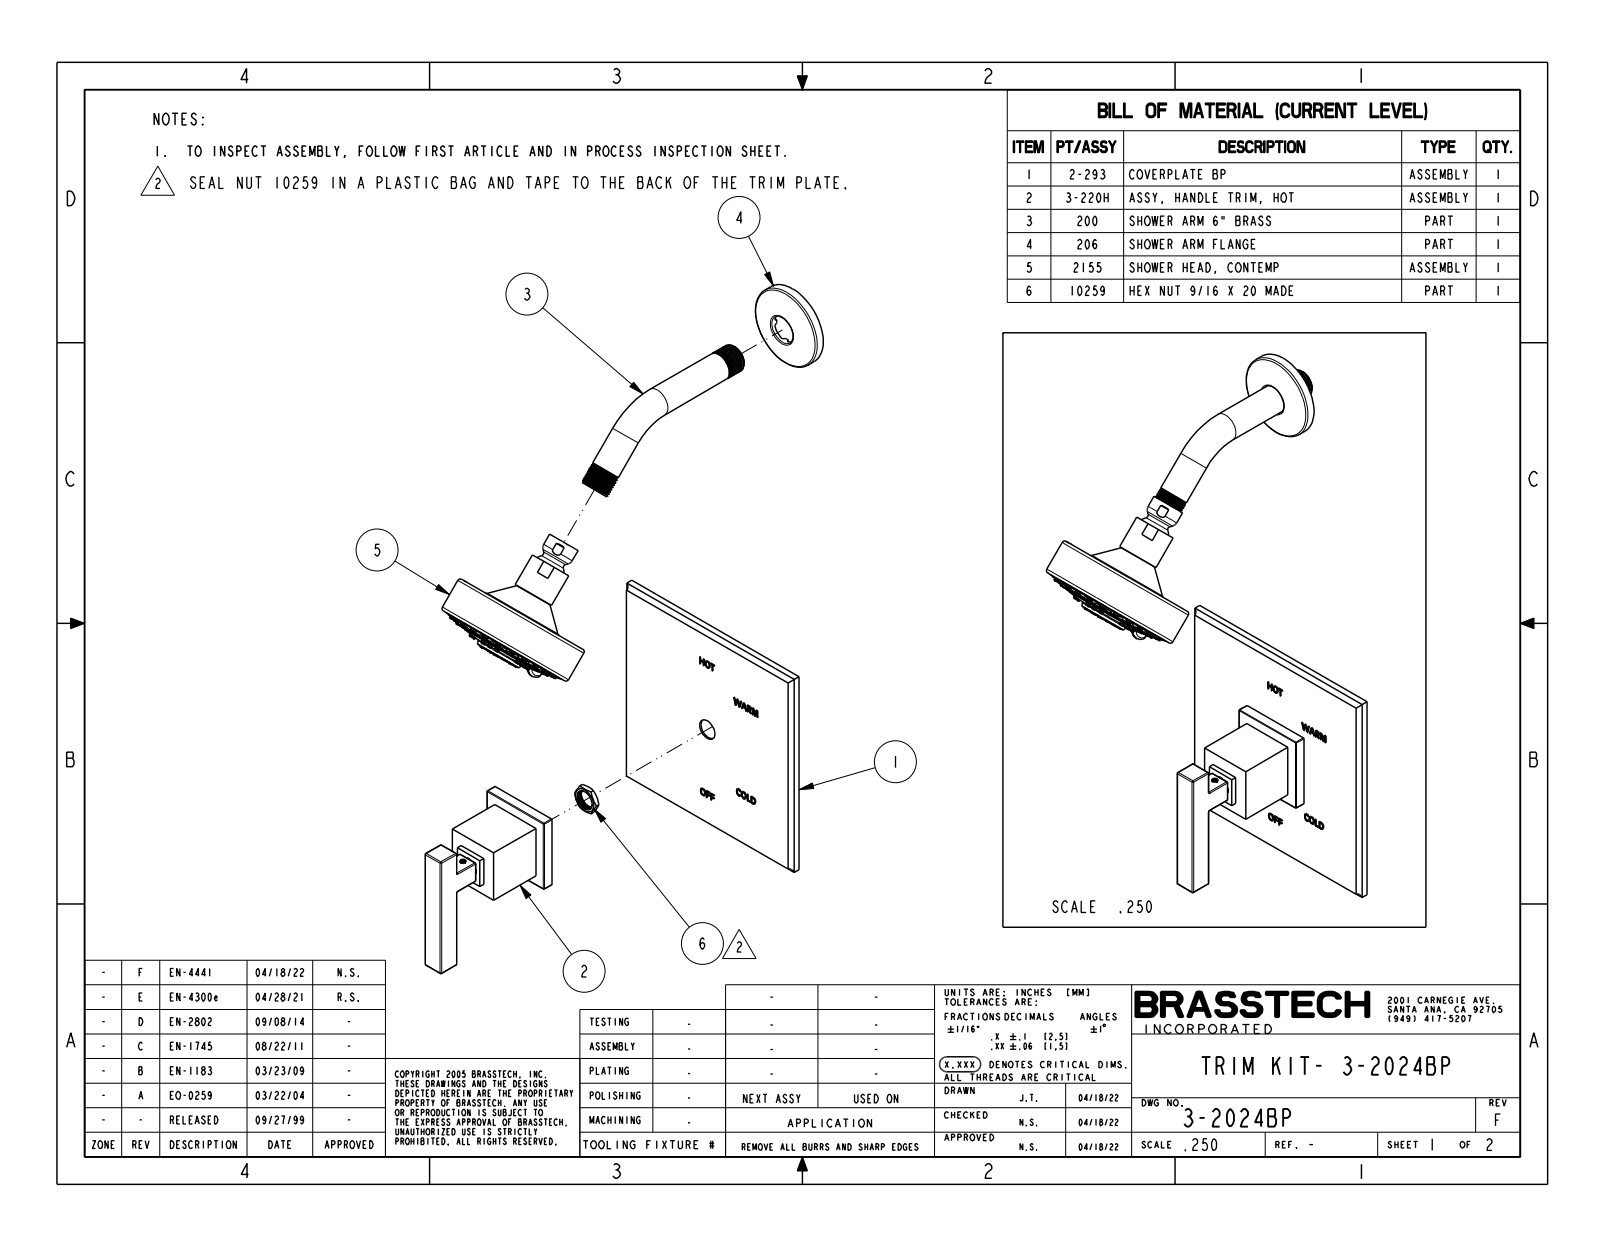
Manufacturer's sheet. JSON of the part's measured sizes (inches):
{"part_name": "3-2024BP", "step_written_by": "CREO PARAMETRIC BY PTC INC, 2018400 (CONFIG_CONTROL_DESIGN)", "units": "inches", "bodies": {"solids": 2, "faces": 1335, "planar": 284, "cylindrical": 230, "other": 821}, "overall_size": [16.44, 8.175, 6.5], "volume_in3": 41.1, "surface_area_in2": 190.7, "round_holes": [[0.059, 8], [0.925, 1]], "round_bosses_or_shafts": [[0.142, 39], [0.165, 23], [0.813, 2], [4, 1], [3.724, 1], [2.38, 1], [2.323, 1], [1.15, 1]], "partial_cylinders_radius": [[0.03, 22], [0.02, 8], [0.079, 8], [0.125, 4], [0.02, 2], [0.138, 1], [0.472, 1], [0.512, 1]], "face_to_face_distances": [0.313, 0.487, 1.113, 1.6, 2.45, 4.05, 0.31, 2.937, 3.563, 0.625], "hole_center_spacings": [0.443, 0.579, 0.818, 0.819, 1.069, 0.443, 0.578, 1.069]}
